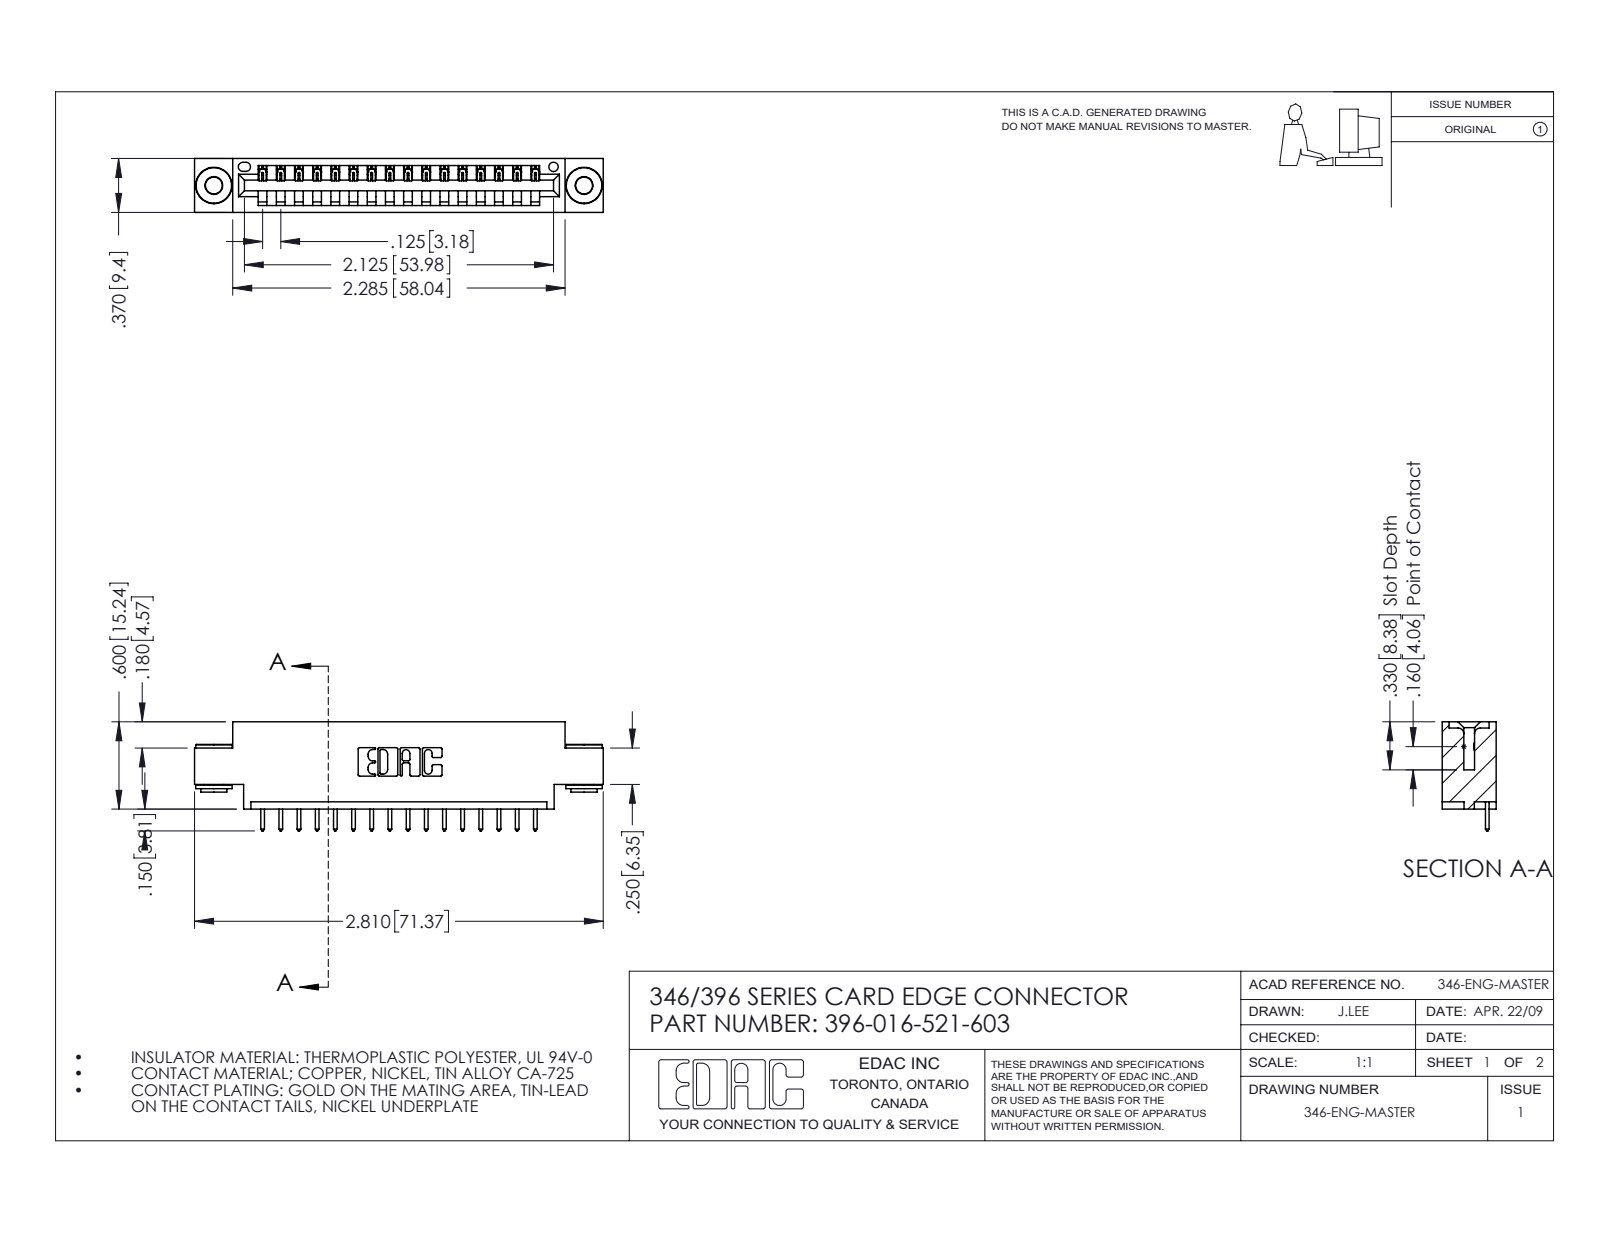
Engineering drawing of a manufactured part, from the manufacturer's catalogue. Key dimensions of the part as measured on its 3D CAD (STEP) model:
Part name (STEP PRODUCT): 346 Part_0.170 Offset - 0.156 Dia-TH; 345-250-002_345-250-002-102; 345-292-001_345-293-121; 396-016-521-603
STEP written by: SolidWorks 2016 (CONFIG_CONTROL_DESIGN)
Units: inches
Bodies: 19 solids, 1092 faces (730 planar, 354 cylindrical, 8 other)
Overall size (bounding box): 2.81 × 0.75 × 0.37
Volume: 0.395 in³ · Surface area: 12.41 in²
Round holes (diameter × count): ⌀0.116 ×2, ⌀0.156 ×2, ⌀0.064 ×1
Round bosses / shafts (diameter × count): ⌀0.25 ×2, ⌀0.18 ×2, ⌀0.136 ×2
Partial cylindrical surfaces — rounded edges, fillets, slot ends (radius × count): R0.006 ×32, R0.01 ×32, R0.01 ×22, R0.007 ×6, R0.031 ×6, R0.026 ×3, R0.031 ×2, R0.04 ×2
Main face-to-face distances: 0.37, 0.048, 0.322, 0.25, 0.025, 0.072, 0.298, 0.148, 0.222, 0.1
Hole centre spacings: 0.246, 2.338, 2.545
